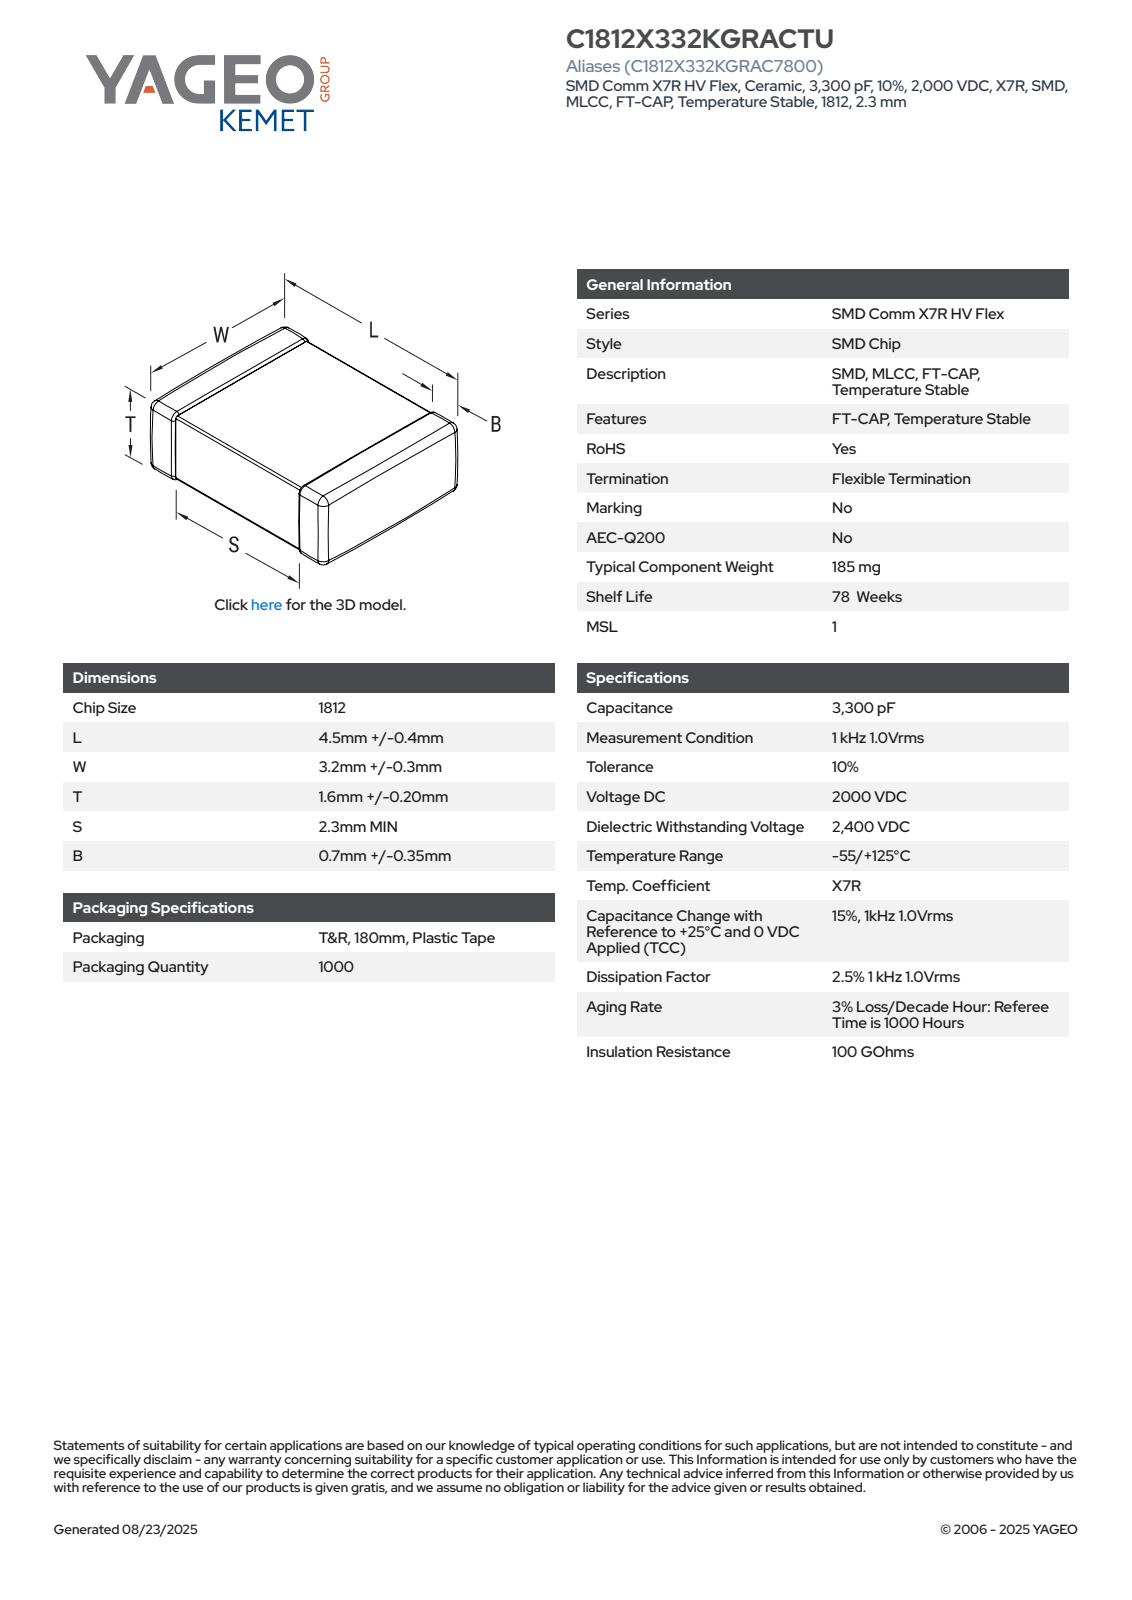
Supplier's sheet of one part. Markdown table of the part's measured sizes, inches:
| quantity | value |
| --- | --- |
| part name | CCS_CCSTDNOS_1812_L4.9W3.5T1.8B1.05 |
| STEP written by | SolidWorks 2014 (AUTOMOTIVE_DESIGN) |
| units | inches |
| bodies | 4 solids, 125 faces (71 planar, 38 cylindrical, 16 other) |
| overall size | 0.193 × 0.138 × 0.071 |
| volume | 0.002 in³ |
| surface area | 0.098 in² |
| main face-to-face distances | 0.068, 0.065, 0.071, 0.135, 0.193, 0.132, 0.138, 0.056, 0.076, 0.059 |
